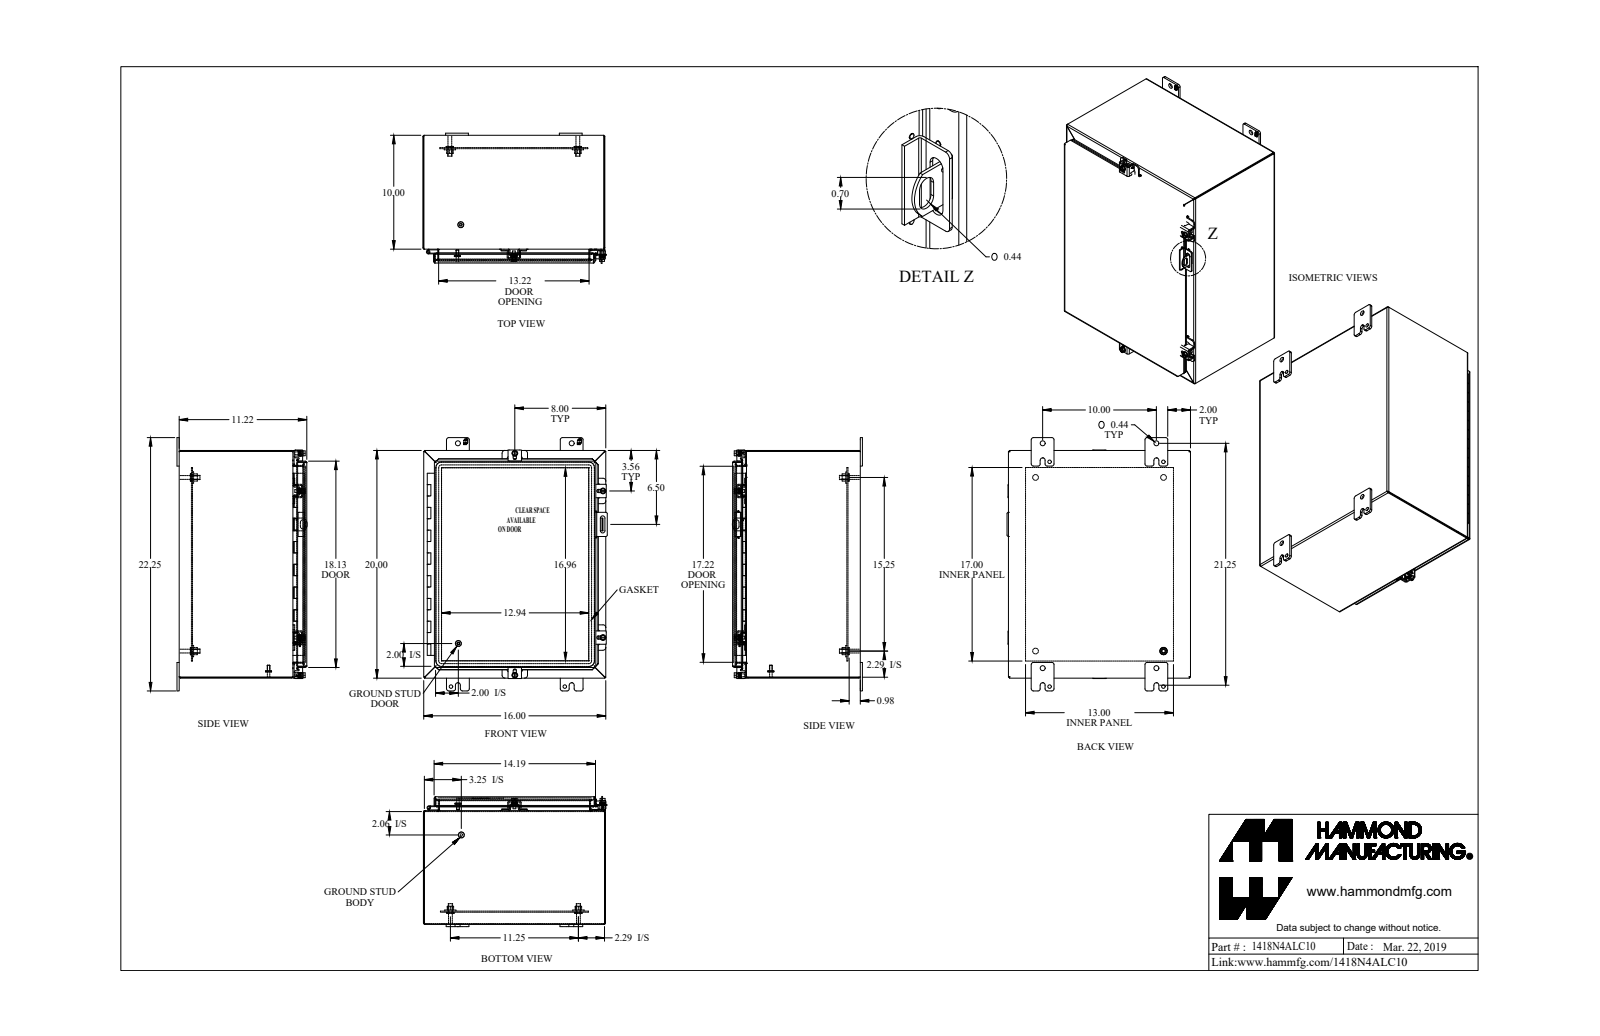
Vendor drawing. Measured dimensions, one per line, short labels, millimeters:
name: 1418N4ALC10_Default
written by: SolidWorks 2019 (CONFIG_CONTROL_DESIGN)
unit: mm
bodies: 38 solids, 1478 faces (879 planar, 489 cylindrical, 110 other)
size: 565.2 × 409.6 × 290.5
volume: 2 663 000 mm³; area: 2 445 000 mm²
holes: 4× ⌀5.9, 4× ⌀6.7, 4× ⌀8, 4× ⌀9.5, 4× ⌀11.1, 4× ⌀12.7, 2× ⌀7.8, 2× ⌀11.3, 1× ⌀3.2, 1× ⌀4.7
bosses: 12× ⌀3.3, 4× ⌀16.5, 4× ⌀12.7, 4× ⌀10.2, 4× ⌀9.5, 4× ⌀8.4, 4× ⌀6.2, 2× ⌀25.4
rounds: 24× R4.8, 22× R1.3, 22× R3.8, 20× R6.4, 16× R1, 16× R3.1, 9× R3.2, 8× R3.6
face distances: 2.1, 404.3, 505.9, 2.5, 280.4, 282.5, 283, 285, 2.4, 255.2
hole spacings: 481.4, 44.1, 254, 463.9, 501.7, 562.3, 61.8, 77.9
